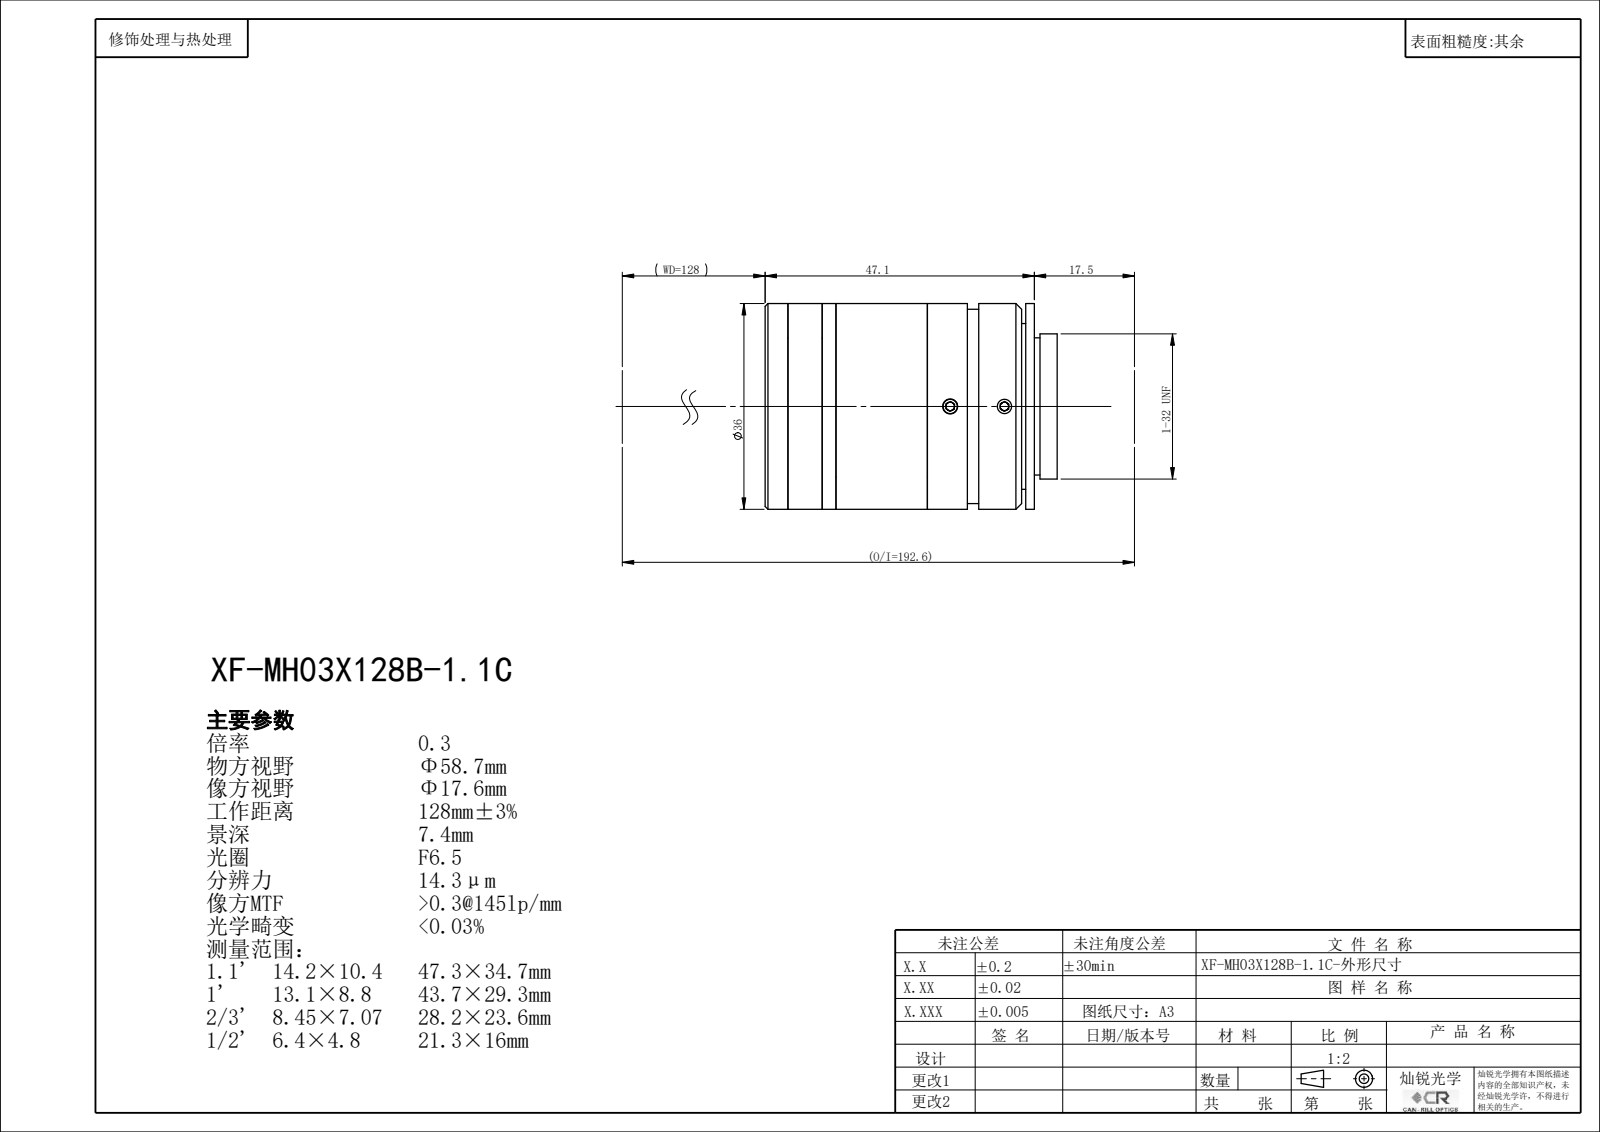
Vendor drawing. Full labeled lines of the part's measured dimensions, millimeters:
Part name (STEP PRODUCT): XF-MH03X128B-1.1C
STEP written by: SolidWorks 2022 (CONFIG_CONTROL_DESIGN)
Units: millimetres
Bodies: 0 solids, 151 faces (75 planar, 42 cylindrical, 34 other)
Overall size (bounding box): 51.13 × 36 × 36
Round holes (diameter × count): ⌀2.5 ×3, ⌀14 ×1, ⌀16.4 ×1, ⌀17 ×1, ⌀18.4 ×1, ⌀22.4 ×1, ⌀24 ×1, ⌀24.9 ×1, ⌀26 ×1
Round bosses / shafts (diameter × count): ⌀36 ×1, ⌀34 ×1, ⌀25.4 ×1
Main face-to-face distances: 18.73, 47.13, 28.4, 1.5, 45.63, 17.23, 41.13, 12.4, 16, 33.23
